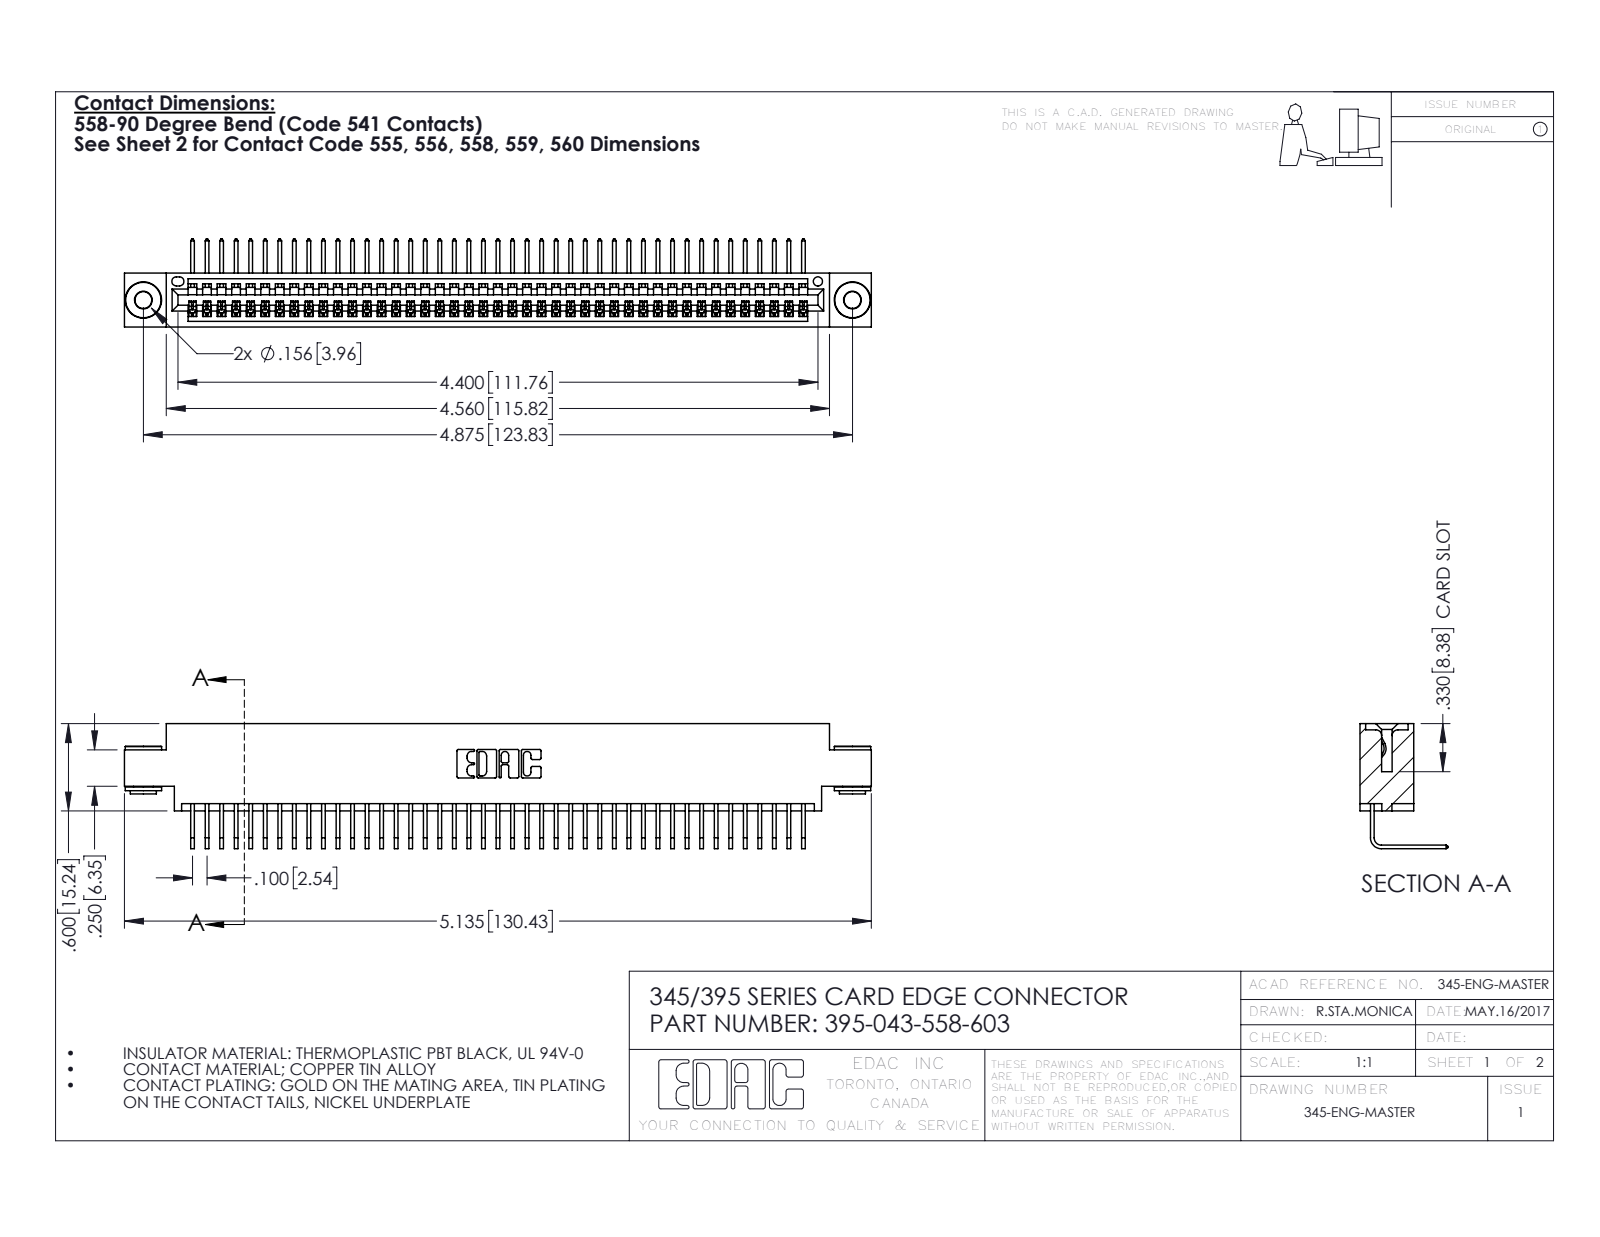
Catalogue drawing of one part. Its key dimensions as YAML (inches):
part_name: "395-043-558-603; 345-250-002_345-250-002-102; 345-292-001_558 Tail - 2; 345 Part_0.170 Offset - 0.156 Dia-TH"
step_written_by: "SolidWorks 2016 (CONFIG_CONTROL_DESIGN)"
units: inches
bodies: {solids: 46, faces: 2748, planar: 1900, cylindrical: 840, other: 8}
overall_size: [5.135, 0.859, 0.605]
volume: 0.759
surface_area: 27.49
round_holes:
  - {diameter: 0.116, count: 2}
  - {diameter: 0.156, count: 2}
  - {diameter: 0.064, count: 1}
round_bosses_or_shafts:
  - {diameter: 0.25, count: 2}
  - {diameter: 0.18, count: 2}
  - {diameter: 0.136, count: 2}
partial_cylinders:
  - {radius: 0.006, count: 86}
  - {radius: 0.01, count: 22}
  - {radius: 0.007, count: 6}
  - {radius: 0.031, count: 6}
  - {radius: 0.026, count: 3}
  - {radius: 0.031, count: 2}
  - {radius: 0.04, count: 2}
  - {radius: 0.014, count: 1}
face_to_face_distances: [0.072, 0.298, 0.37, 0.2, 0.098, 0.272, 0.025, 0.225, 0.175, 0.149]
hole_center_spacings: [0.27, 4.639, 4.875]
